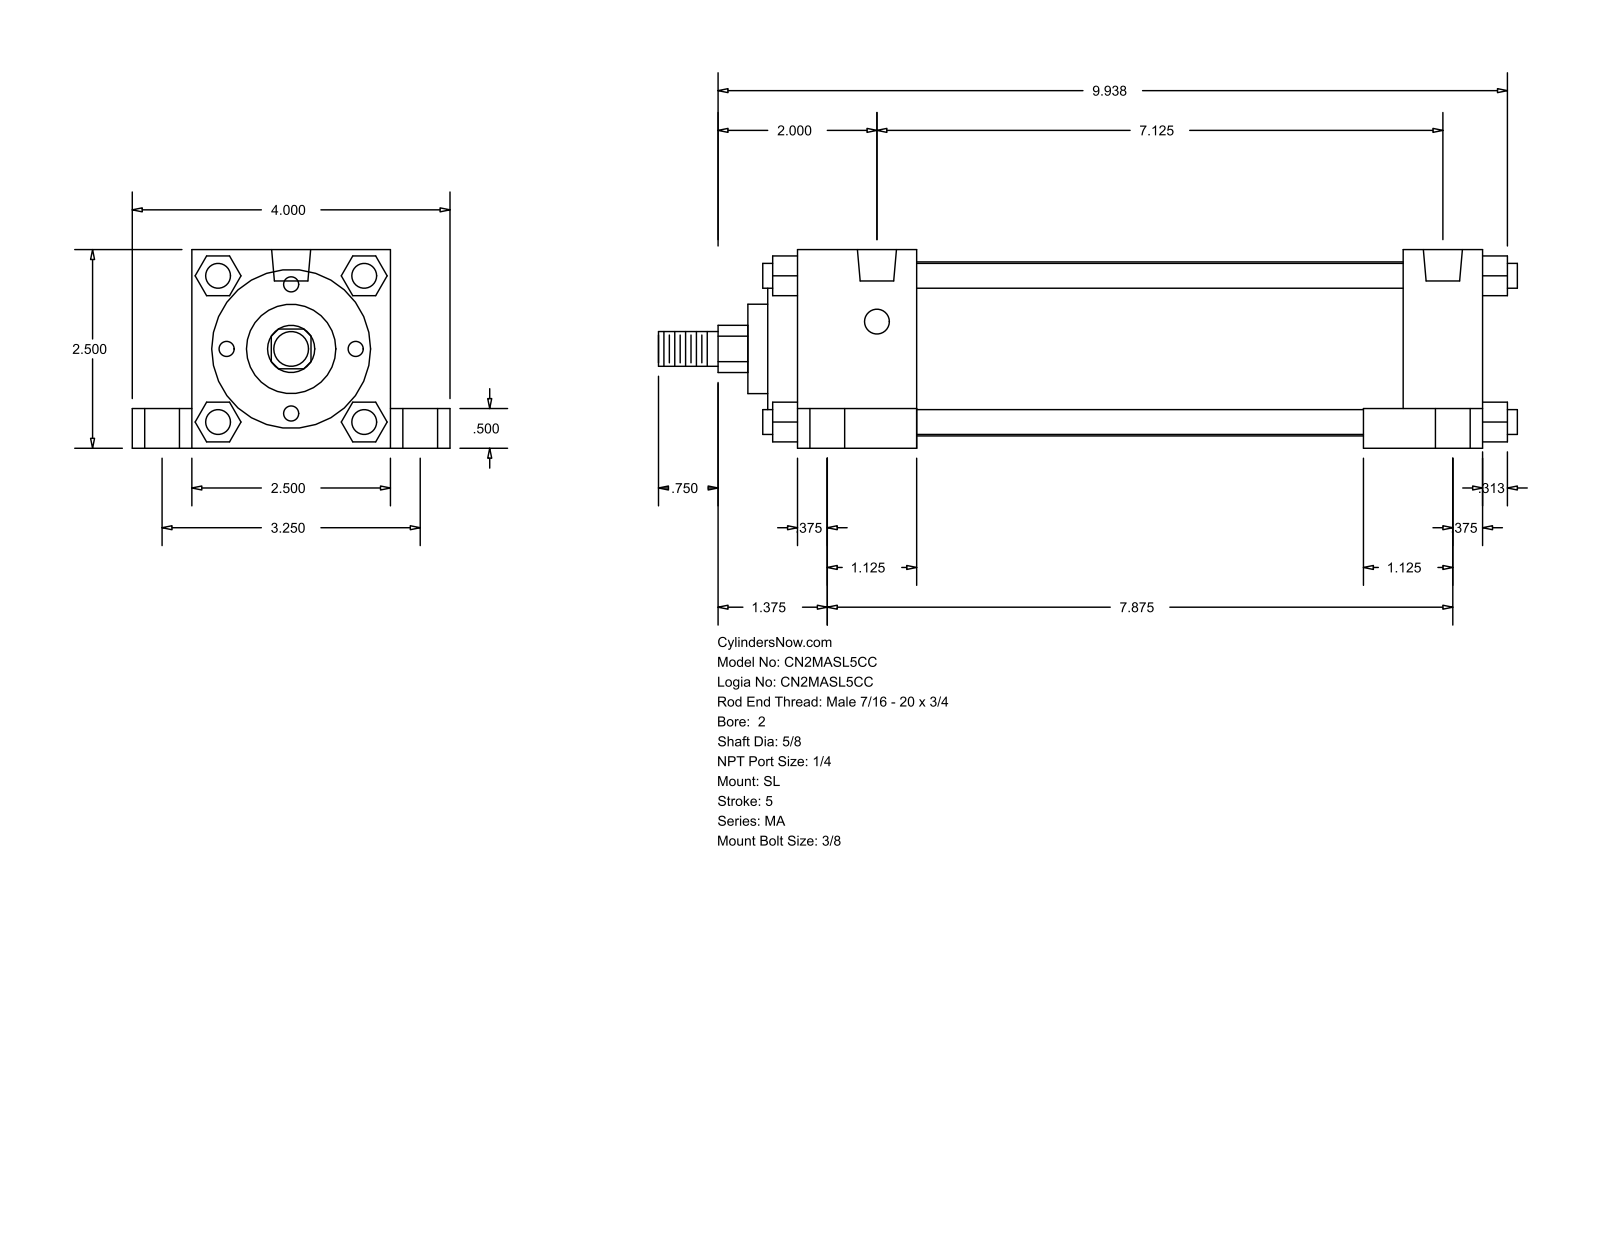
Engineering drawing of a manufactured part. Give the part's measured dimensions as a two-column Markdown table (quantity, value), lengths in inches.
| quantity | value |
| --- | --- |
| part name | MA_SL__0200_0.625 |
| STEP written by | GSSL Pune (CONFIG_CONTROL_DESIGN) |
| units | inches |
| bodies | 0 solids, 150 faces (113 planar, 37 cylindrical, 0 other) |
| overall size | 10.813 × 4 × 2.5 |
| round holes (diameter × count) | 0.313 × 4, 0.437 × 4, 0.687 × 4, 0.492 × 2 |
| round bosses / shafts (diameter × count) | 0.313 × 4, 2.19 × 1, 2 × 1, 1.125 × 1, 0.625 × 1, 0.437 × 1 |
| partial cylindrical surfaces (radius × count) | 0.297 × 1 |
| main face-to-face distances | 2.5, 0.5, 0.375, 6.125, 1, 0.75, 3.25, 1.5, 8.625, 2 |
| hole center spacings | 1.63, 1.741, 3.25, 7.125, 7.43, 7.875, 7.919, 8.519 |
